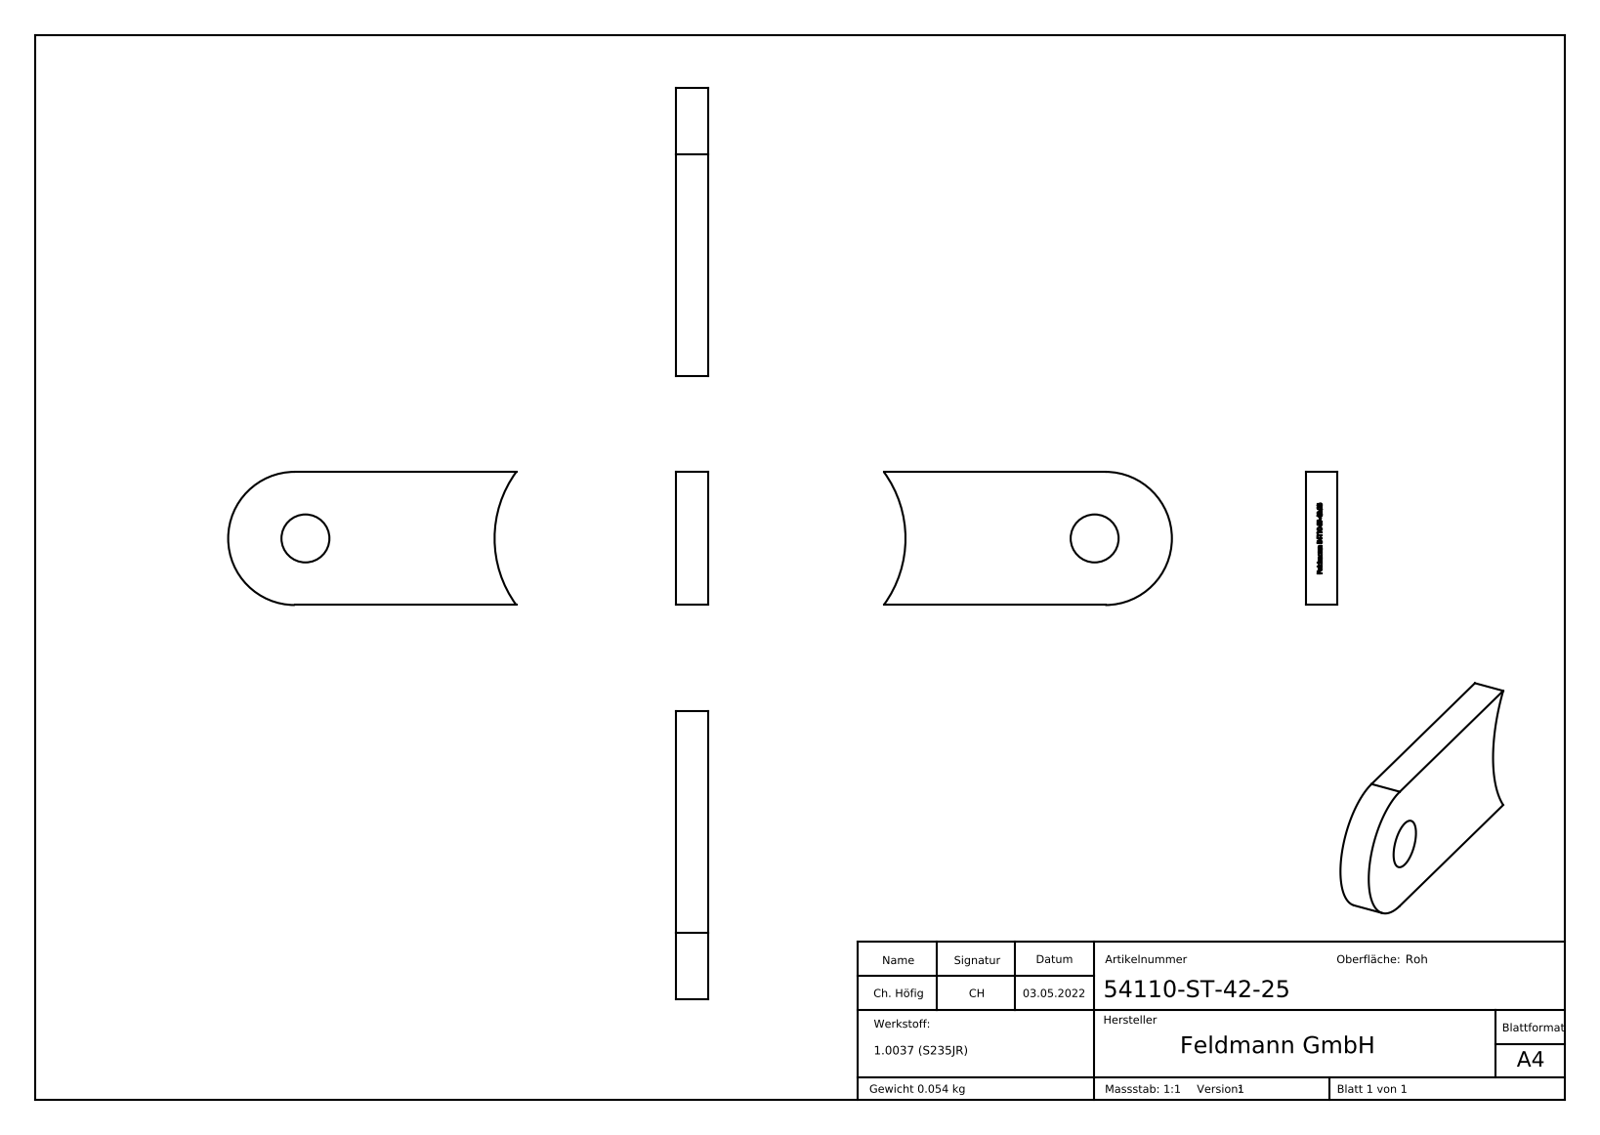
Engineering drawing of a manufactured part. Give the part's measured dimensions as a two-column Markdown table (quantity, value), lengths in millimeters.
| quantity | value |
| --- | --- |
| part name | 54110-ST-42-25 |
| STEP written by | SolidWorks 2018 (CONFIG_CONTROL_DESIGN) |
| units | millimeters |
| bodies | 1 solid, 273 faces (142 planar, 31 cylindrical, 100 other) |
| overall size | 54.08 × 25 × 6 |
| volume | 6 911 mm³ |
| surface area | 3 375 mm² |
| round holes (diameter × count) | 9 × 1 |
| partial cylindrical surfaces (radius × count) | 12.5 × 1, 21.2 × 1, 21.3 × 1 |
| main face-to-face distances | 6, 25, 3, 0.71, 0.53, 3.79, 2.66, 0.44, 0.61, 0.79 |
